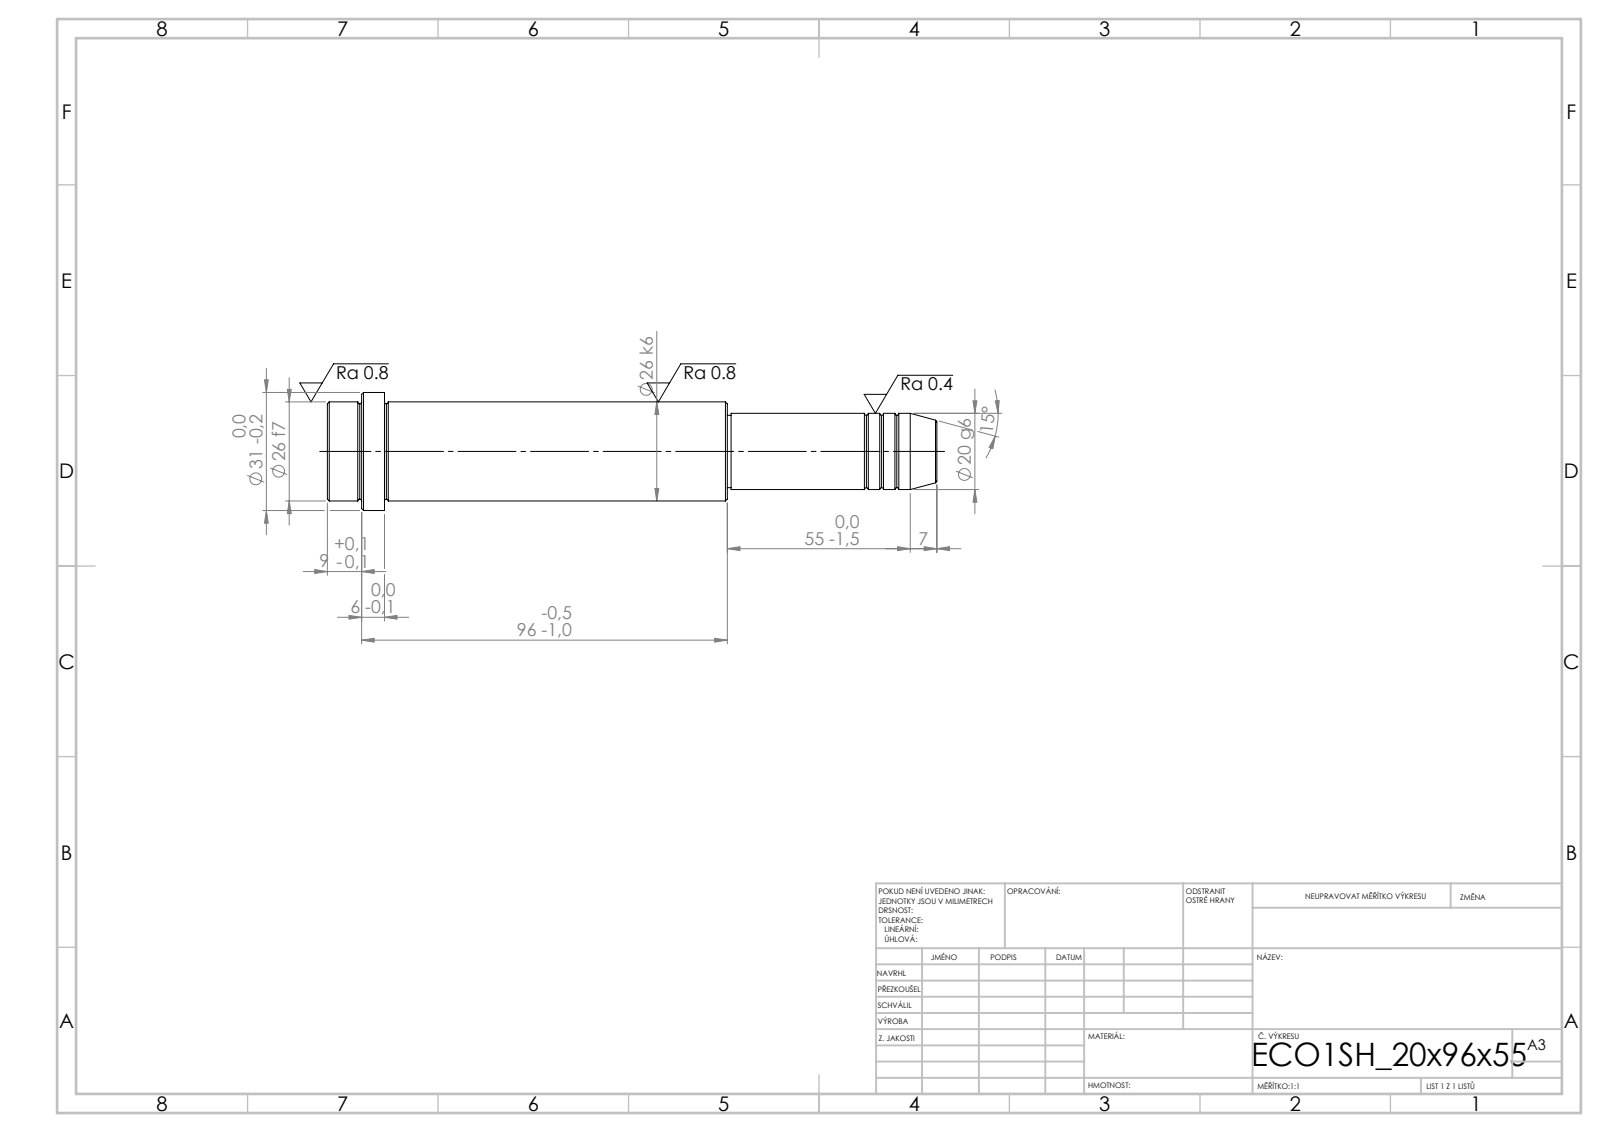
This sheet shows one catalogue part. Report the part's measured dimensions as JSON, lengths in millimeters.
{"step_written_by": "SolidWorks 2019 (CONFIG_CONTROL_DESIGN)", "units": "millimeters", "bodies": {"solids": 1, "faces": 52, "planar": 6, "cylindrical": 16, "other": 30}, "overall_size": [160, 31, 31], "volume_mm3": 73783, "surface_area_mm2": 13662, "round_bosses_or_shafts": [[31, 1], [26, 1], [20, 1], [19, 1]], "face_to_face_distances": [15, 90, 105, 55, 145, 160, 151, 96, 6, 9]}
